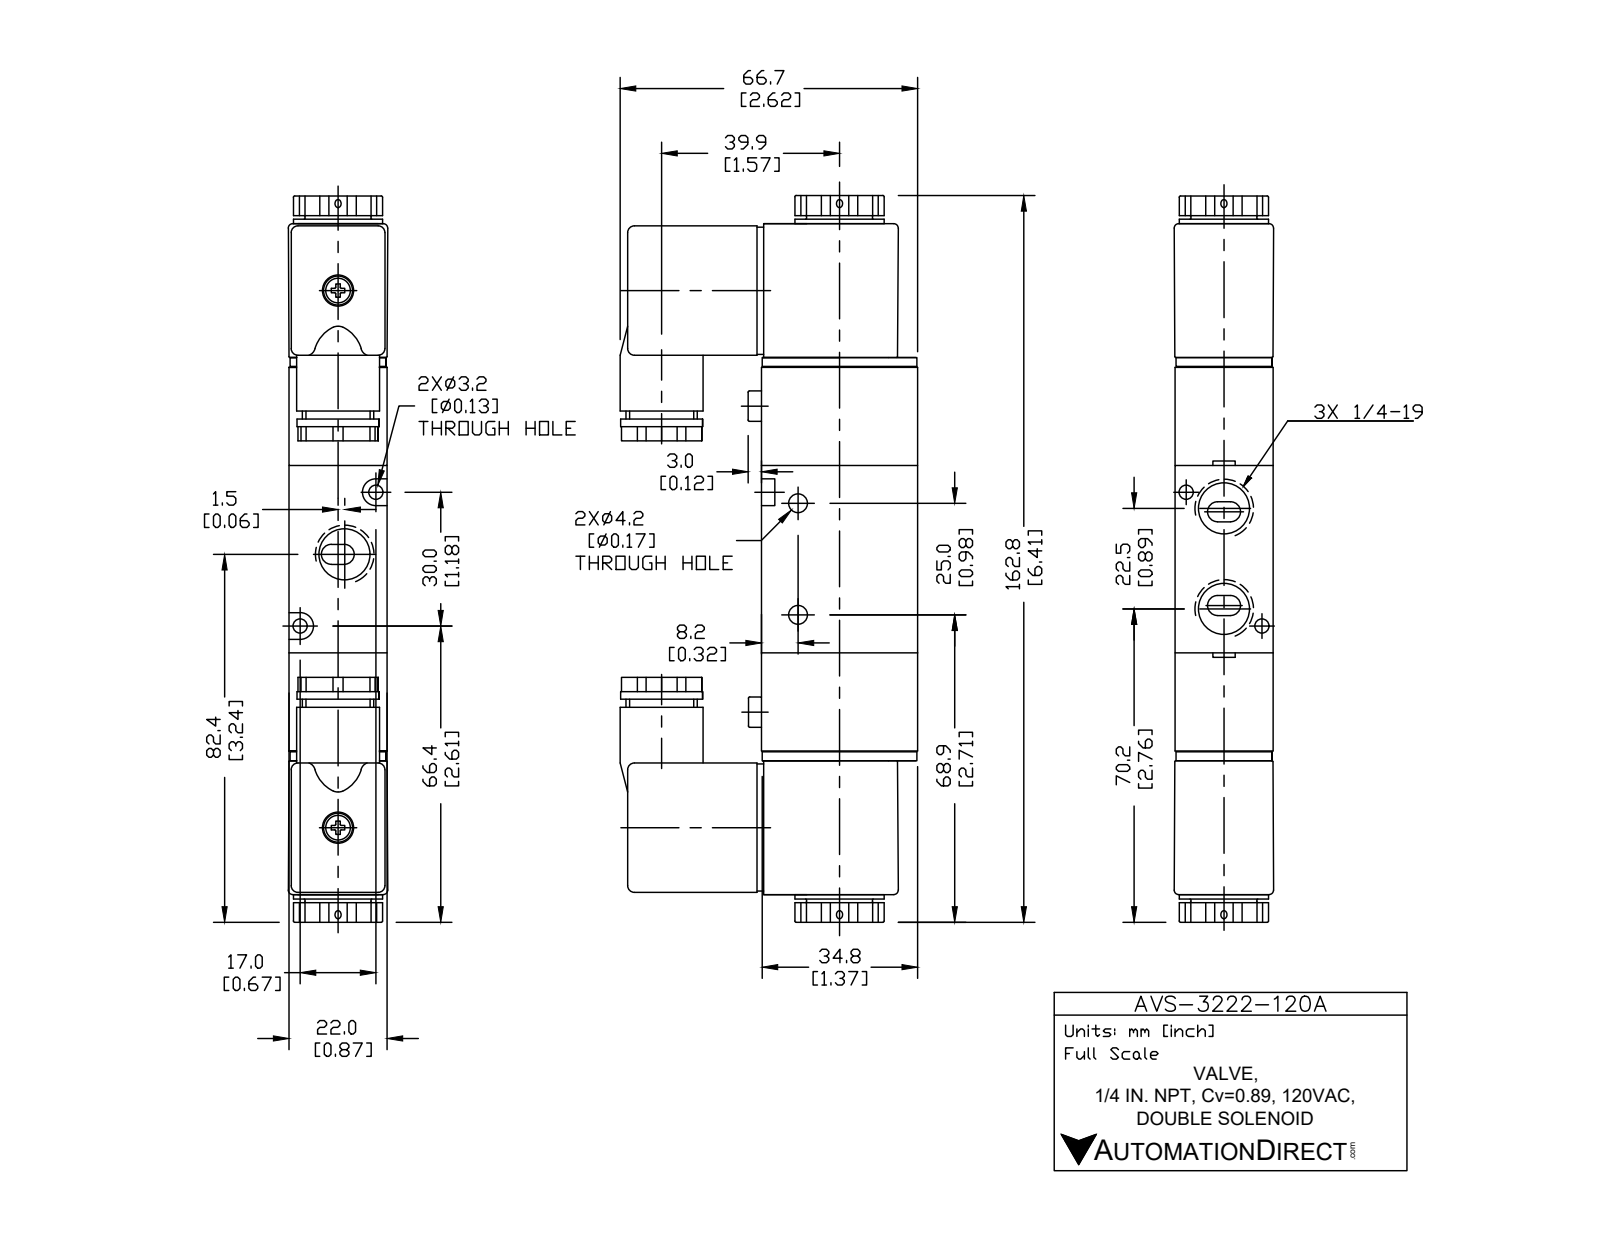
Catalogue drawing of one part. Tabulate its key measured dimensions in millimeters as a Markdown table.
| quantity | value |
| --- | --- |
| part name | AVS-3222-120A |
| STEP written by | SolidWorks 2015 (CONFIG_CONTROL_DESIGN) |
| units | millimeters |
| bodies | 5 solids, 252 faces (138 planar, 82 cylindrical, 32 other) |
| overall size | 162.8 × 66.7 × 22 |
| volume | 150 909 mm³ |
| surface area | 34 488 mm² |
| round holes (diameter × count) | 11.13 × 3, 3.3 × 2, 4.3 × 2, 9.3 × 1 |
| round bosses / shafts (diameter × count) | 6.8 × 2, 20 × 1, 18.6 × 1, 18.4 × 1, 16 × 1, 14.8 × 1 |
| partial cylindrical surfaces (radius × count) | 1 × 20, 0.5 × 12, 3 × 2 |
| main face-to-face distances | 0.5, 22.6, 21.5, 21, 42, 22.82, 22.38, 22, 53.7, 95.7 |
| hole center spacings | 9.27, 9.31, 10.41, 12.29, 15.65, 18.87, 22.5, 25 |
